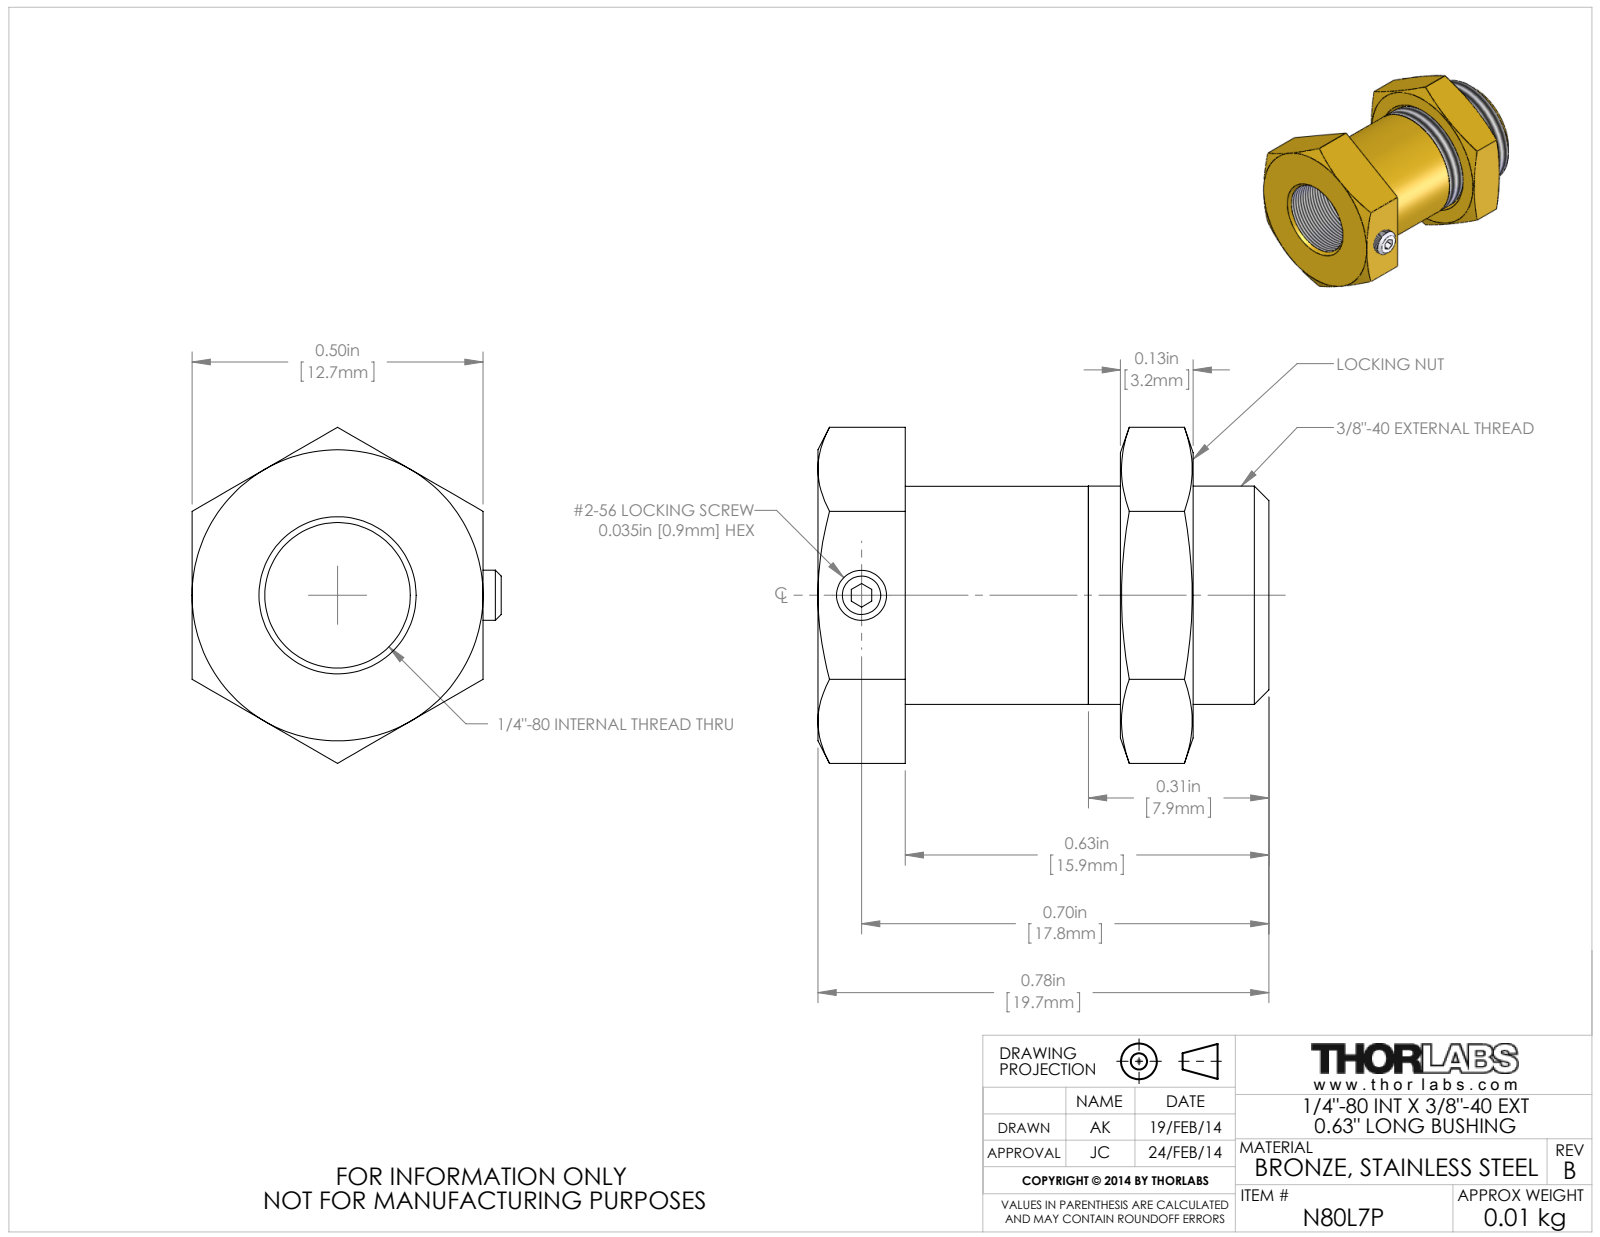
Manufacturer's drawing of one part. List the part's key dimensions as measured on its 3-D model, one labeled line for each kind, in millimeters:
Part name (STEP PRODUCT): 19451-E0W
STEP written by: SolidWorks 2007 (AUTOMOTIVE_DESIGN)
Units: millimetres
Bodies: 3 solids, 70 faces (27 planar, 14 cylindrical, 29 other)
Overall size (bounding box): 19.68 × 14.66 × 13.49
Volume: 1 244 mm³ · Surface area: 1 623 mm²
Round holes (diameter × count): ⌀1.78 ×1, ⌀6.35 ×1, ⌀9.53 ×1
Round bosses / shafts (diameter × count): ⌀9.51 ×1, ⌀2.18 ×1, ⌀0.79 ×1
Main face-to-face distances: 12.7, 3.81, 3.17, 12.57, 16.38, 9.4, 13.21, 3.3, 6.47, 15.87
